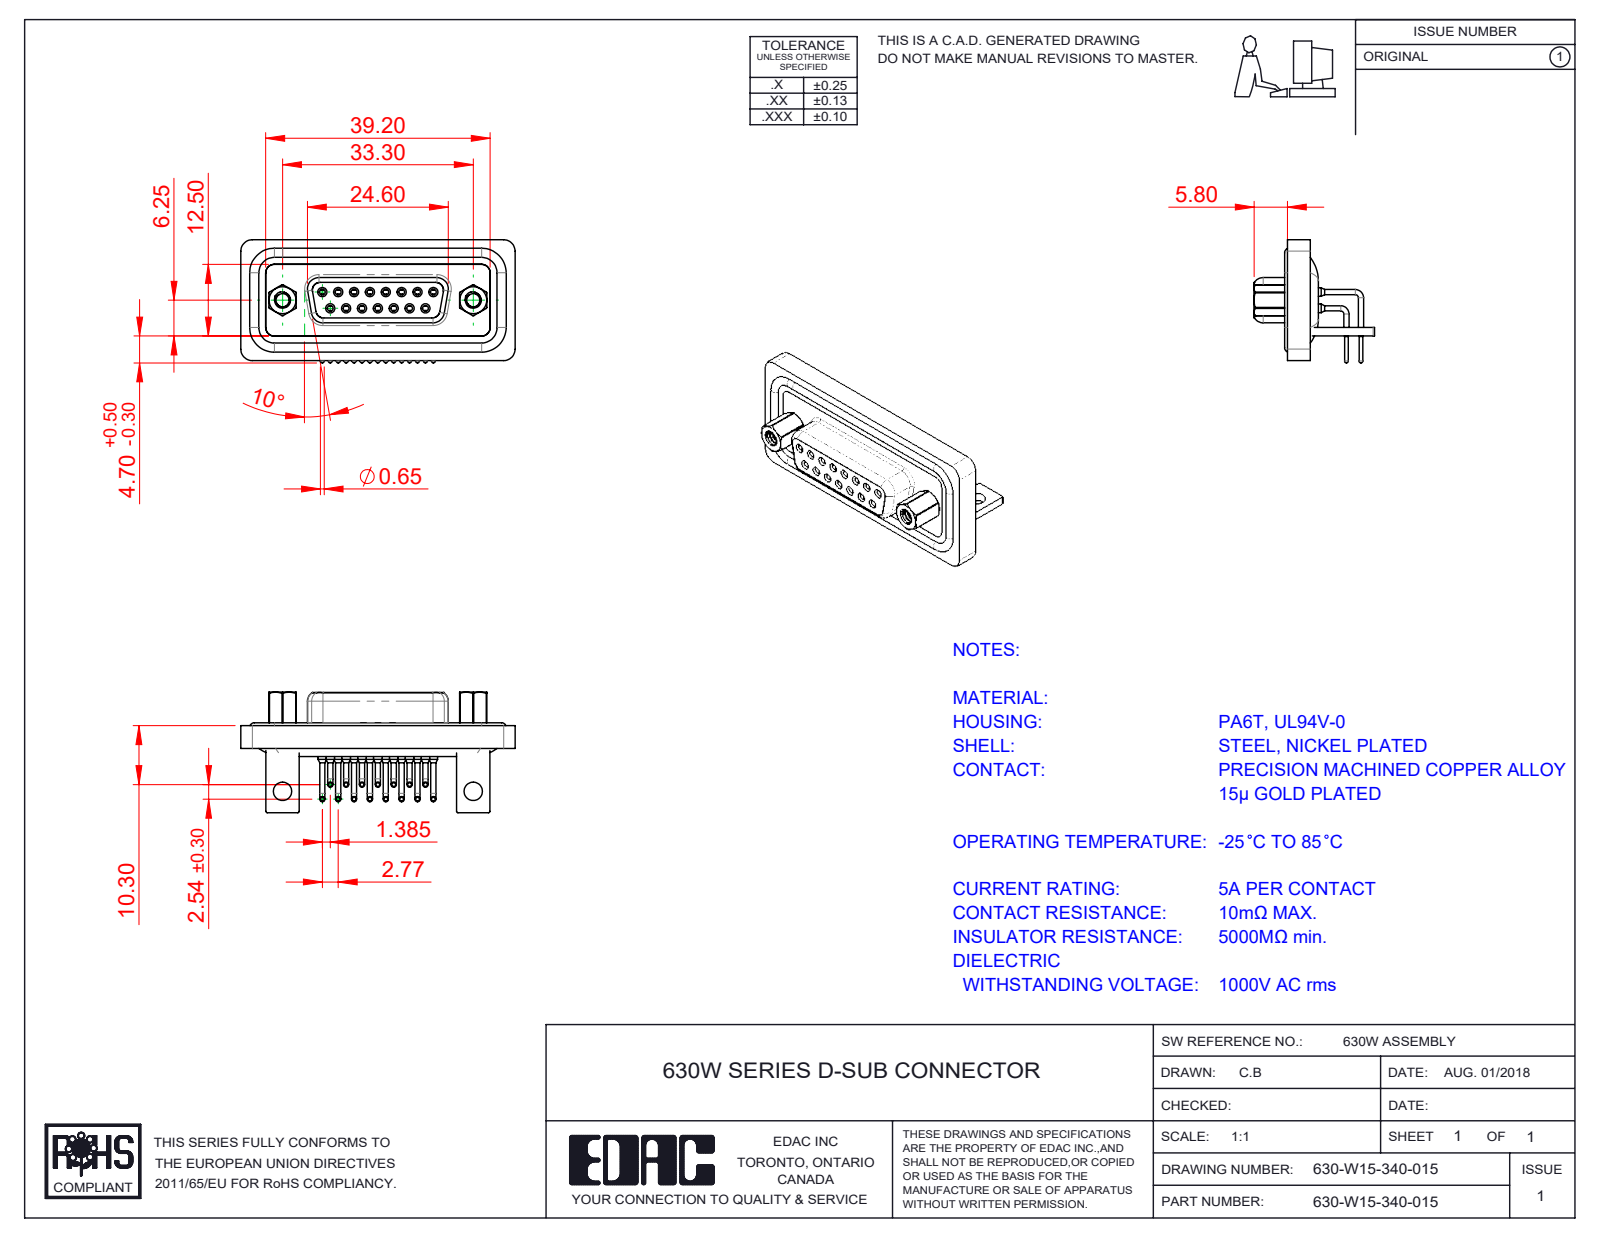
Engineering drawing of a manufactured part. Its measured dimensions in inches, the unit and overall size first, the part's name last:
Units: inches
Overall size (bounding box): 1.885 × 0.846 × 0.846
Round holes (diameter × count): ⌀0.039 ×15, ⌀0.043 ×15, ⌀0.059 ×15, ⌀0.067 ×15, ⌀0.071 ×15, ⌀0.079 ×15, ⌀0.089 ×2, ⌀0.09 ×2, ⌀0.126 ×2, ⌀0.157 ×2, ⌀0.189 ×2, ⌀0.193 ×2
Round bosses / shafts (diameter × count): ⌀0.035 ×30, ⌀0.063 ×19, ⌀0.059 ×15, ⌀0.026 ×15, ⌀0.11 ×2, ⌀0.197 ×1
Partial cylindrical surfaces — rounded edges, fillets, slot ends (radius × count): R0.079 ×17, R0.059 ×14, R0.01 ×12, R0.053 ×8, R0.106 ×6, R0.02 ×5, R0.035 ×4, R0.063 ×4
Main face-to-face distances: 0.016, 0.071, 0.063, 0.043, 0.169, 0.098, 0.114, 0.386, 0.02, 0.059
Hole centre spacings: 0.124, 0.109, 0.218, 0.327, 0.125, 0.124, 0.436, 0.198
Volume: 0.358 in³ · Surface area: 16.03 in²
Bodies: 25 solids, 1296 faces (348 planar, 619 cylindrical, 329 other)
Part name (STEP PRODUCT): 630W Waterproof Housing_15 Contacts; 630W Housing_15 Contacts; 630W Contact Row 1; 630-W15-340-015 (+5 more)
STEP written by: SolidWorks 2023 (CONFIG_CONTROL_DESIGN)
